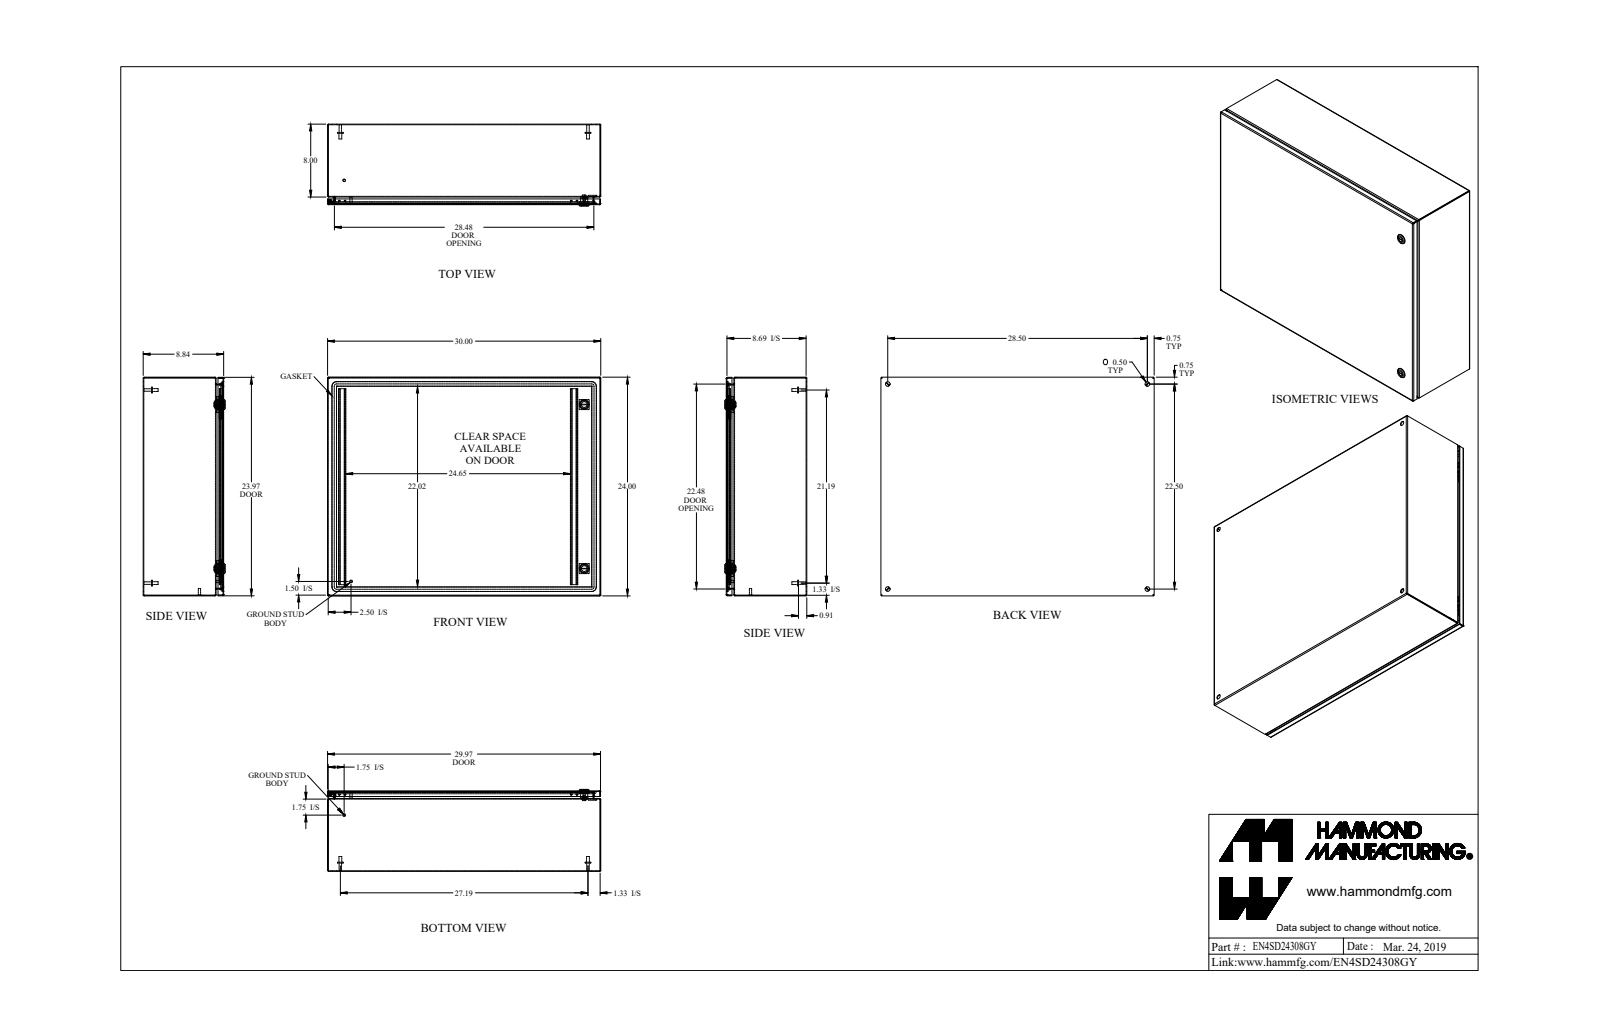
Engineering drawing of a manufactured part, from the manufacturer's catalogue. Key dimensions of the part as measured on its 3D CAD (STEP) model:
Part name (STEP PRODUCT): EN4SD24308GY_Default
STEP written by: SolidWorks 2019 (CONFIG_CONTROL_DESIGN)
Units: inches
Bodies: 27 solids, 783 faces (386 planar, 257 cylindrical, 140 other)
Overall size (bounding box): 30 × 24 × 8.997
Volume: 194.3 in³ · Surface area: 5 429 in²
Round holes (diameter × count): ⌀0.5 ×4, ⌀0.232 ×2, ⌀0.625 ×2, ⌀0.785 ×2, ⌀0.172 ×1, ⌀0.24 ×1, ⌀0.242 ×1
Round bosses / shafts (diameter × count): ⌀0.625 ×4, ⌀0.313 ×4, ⌀0.27 ×4, ⌀1.1 ×2, ⌀0.525 ×2, ⌀0.281 ×2, ⌀0.25 ×2, ⌀0.455 ×1
Partial cylindrical surfaces — rounded edges, fillets, slot ends (radius × count): R0.036 ×20, R0.108 ×20, R0.043 ×12, R0.081 ×12, R0.382 ×12, R19.003 ×8, R0.006 ×4, R0.062 ×4
Main face-to-face distances: 0.072, 8.765, 8.693, 8.837, 23.928, 29.928, 23.856, 24, 29.856, 30
Hole centre spacings: 22.5, 27.519, 28.5, 36.311, 2.493, 2.494, 17.999, 20.277
